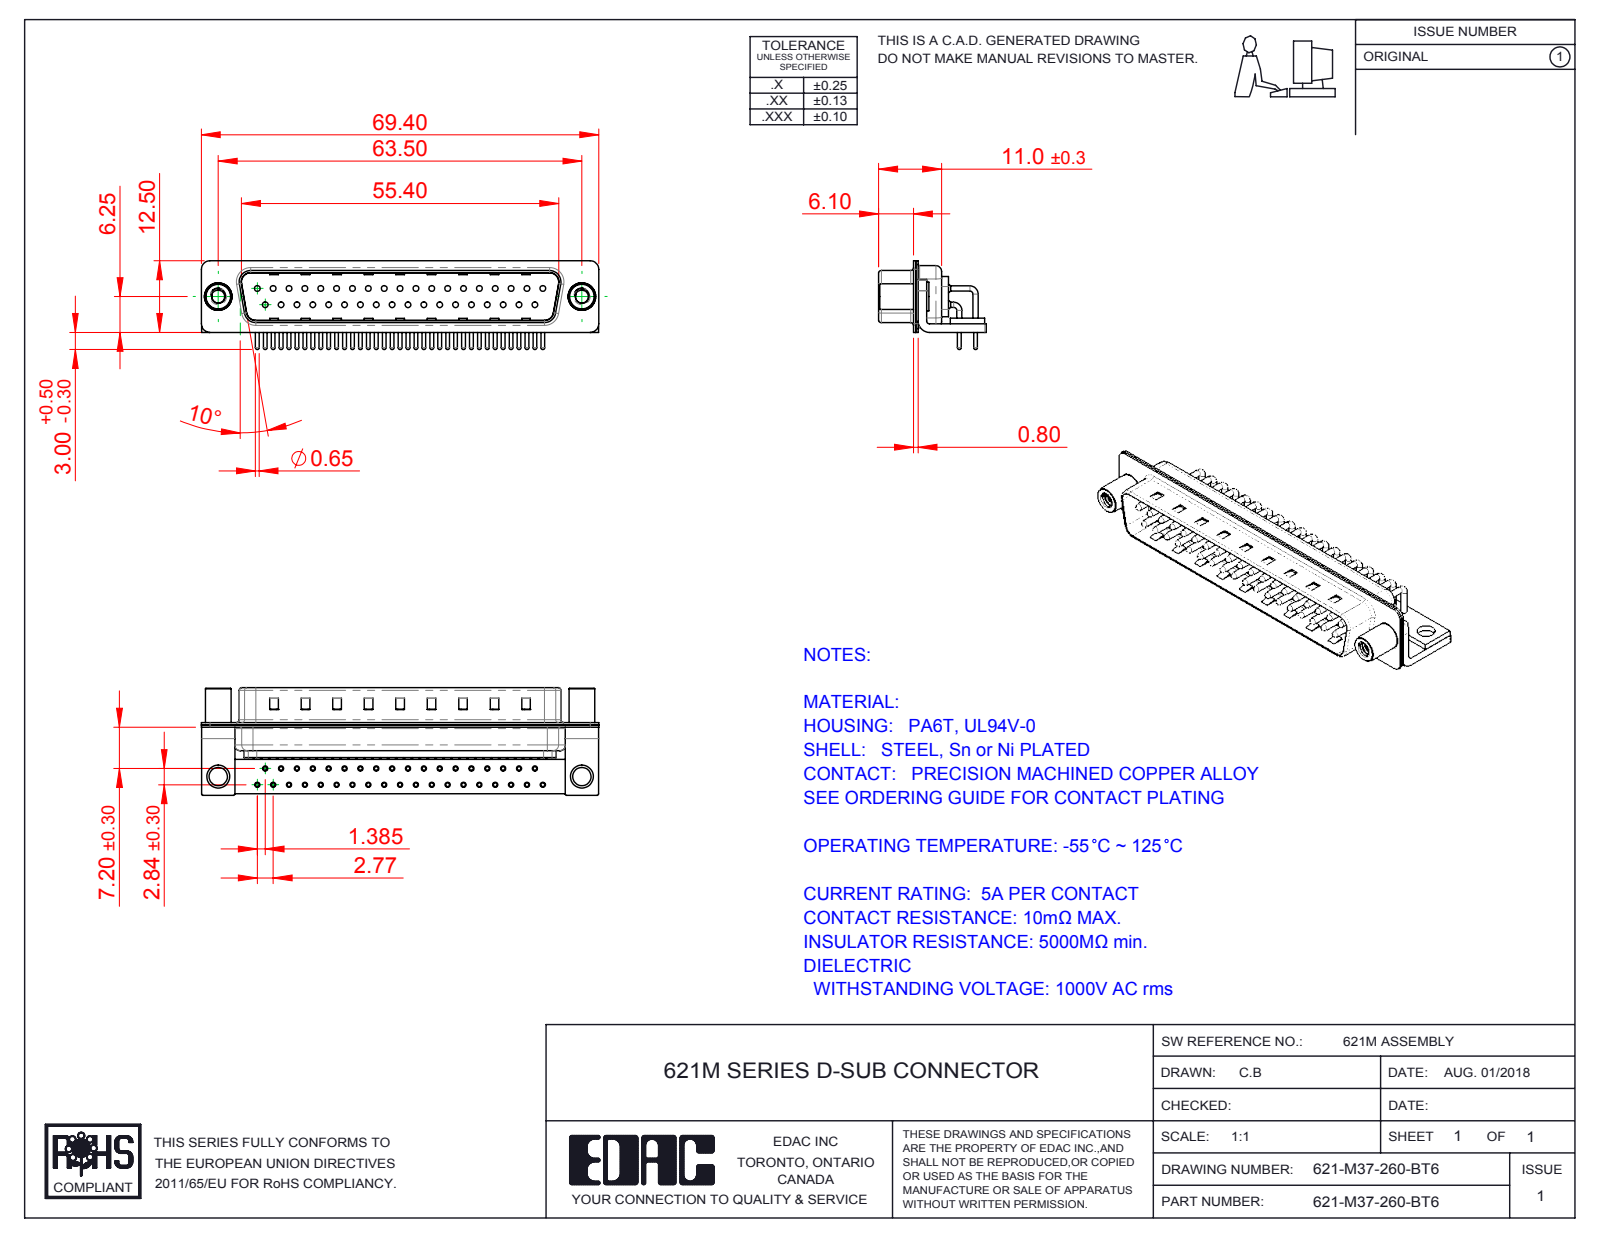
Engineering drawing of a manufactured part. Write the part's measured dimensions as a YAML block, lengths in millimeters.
part_name: "621M Shell Front_37 Contacts; 621M Shell Rear_37 Contacts; 621M Contact Row 1; 621M Stabilizer Bracket (+5 more)"
step_written_by: "SolidWorks 2016 (CONFIG_CONTROL_DESIGN)"
units: millimeters
bodies: {solids: 45, faces: 4656, planar: 2599, cylindrical: 1611, other: 446}
overall_size: [69.4, 18.8, 15.49]
volume: 4724
surface_area: 12233
round_holes:
  - {diameter: 0.9, count: 37}
  - {diameter: 1, count: 37}
  - {diameter: 1.7, count: 37}
  - {diameter: 2, count: 37}
  - {diameter: 2.26, count: 2}
  - {diameter: 3.2, count: 2}
  - {diameter: 4, count: 2}
  - {diameter: 4.8, count: 2}
round_bosses_or_shafts:
  - {diameter: 0.9, count: 46}
  - {diameter: 1.5, count: 37}
  - {diameter: 0.65, count: 37}
  - {diameter: 5, count: 2}
  - {diameter: 4.9, count: 2}
  - {diameter: 4.5, count: 2}
partial_cylinders:
  - {radius: 1.01, count: 37}
  - {radius: 0.25, count: 16}
  - {radius: 1.5, count: 16}
  - {radius: 2, count: 13}
  - {radius: 0.5, count: 9}
  - {radius: 1.6, count: 8}
  - {radius: 0.6, count: 4}
  - {radius: 0.65, count: 4}
face_to_face_distances: [0.4, 0.85, 1.25, 9.55, 1.5, 8.3, 0.8, 10.4, 8.7, 1]
hole_center_spacings: [3.16, 2.77, 5.54, 8.31, 11.08, 13.85, 5.03, 16.62]
